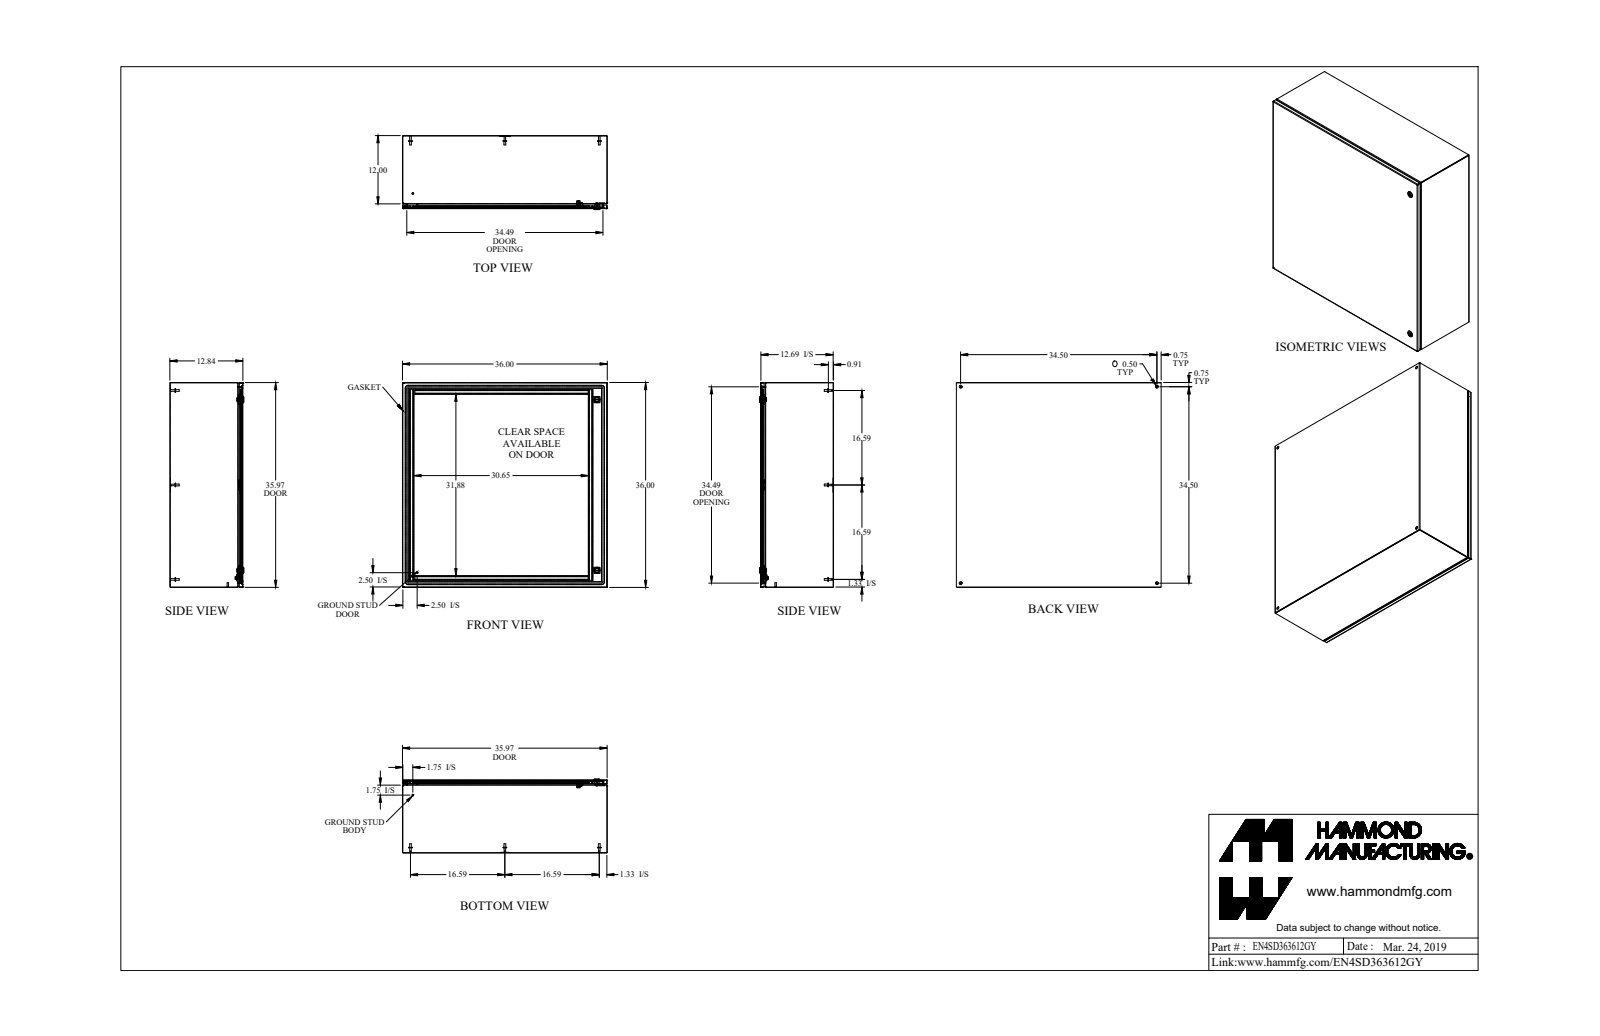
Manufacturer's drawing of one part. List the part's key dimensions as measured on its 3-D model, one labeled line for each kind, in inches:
Part name (STEP PRODUCT): EN4SD363612GY
STEP written by: SolidWorks 2019 (AUTOMOTIVE_DESIGN)
Units: inches
Bodies: 43 solids, 1176 faces (559 planar, 394 cylindrical, 223 other)
Overall size (bounding box): 36 × 36 × 12.997
Volume: 354.9 in³ · Surface area: 10 029 in²
Round holes (diameter × count): ⌀0.5 ×4, ⌀0.232 ×2, ⌀0.625 ×2, ⌀0.785 ×2, ⌀0.172 ×1, ⌀0.196 ×1, ⌀0.24 ×1, ⌀0.242 ×1, ⌀0.275 ×1, ⌀0.375 ×1
Round bosses / shafts (diameter × count): ⌀0.313 ×8, ⌀0.27 ×8, ⌀0.625 ×6, ⌀0.625 ×3, ⌀1.1 ×2, ⌀0.525 ×2, ⌀0.281 ×2, ⌀0.25 ×2
Partial cylindrical surfaces — rounded edges, fillets, slot ends (radius × count): R0.043 ×24, R0.081 ×24, R0.036 ×18, R0.108 ×18, R0.312 ×12, R0.062 ×10, R0.094 ×10, R0.016 ×9
Main face-to-face distances: 0.072, 12.765, 35.928, 12.693, 12.837, 35.856, 36, 0.837, 11.928, 0.038
Hole centre spacings: 34.5, 33.502, 48.791, 2.493, 2.494, 3.542, 4.442, 29.999
